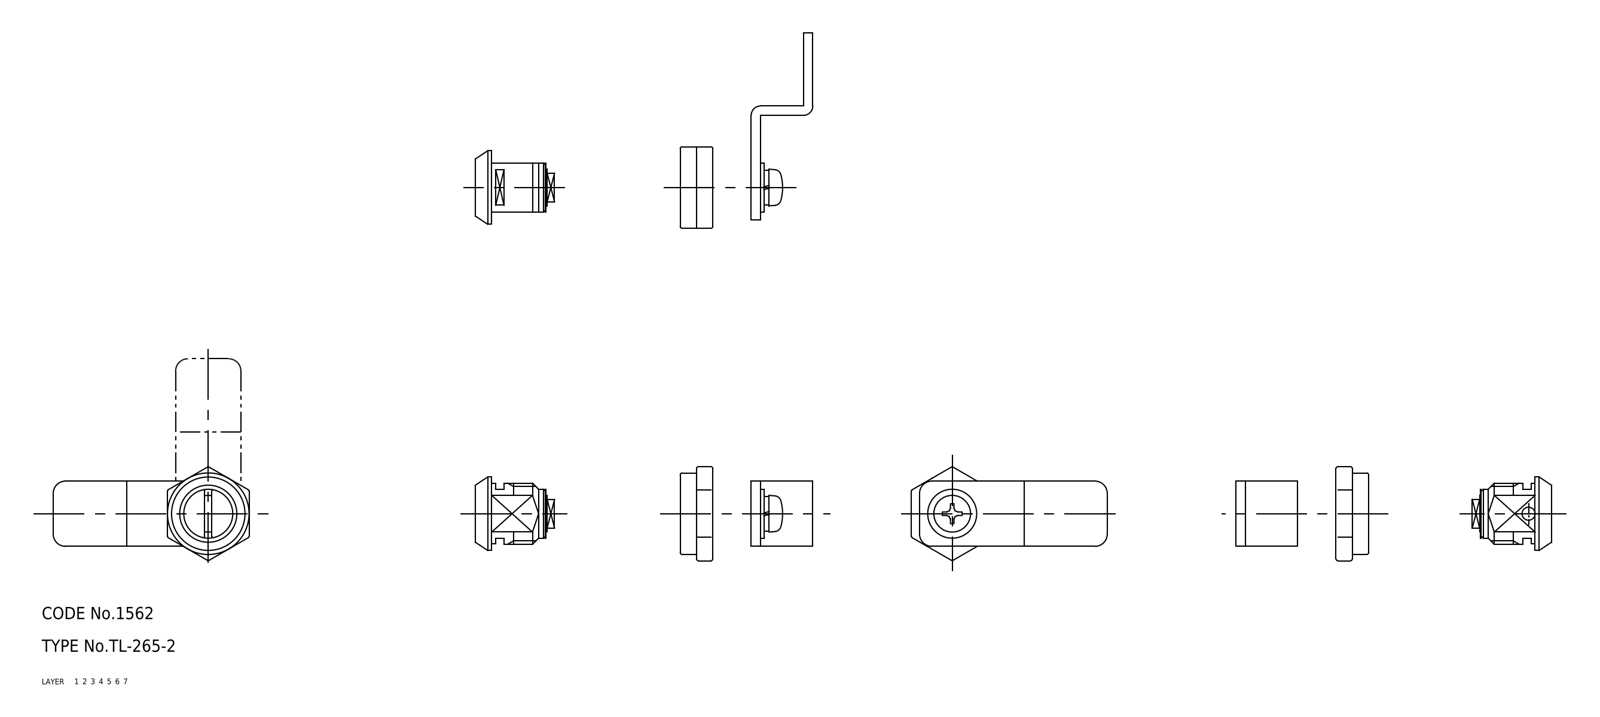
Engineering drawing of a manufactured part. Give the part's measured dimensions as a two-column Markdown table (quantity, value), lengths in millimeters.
| quantity | value |
| --- | --- |
| part name | shaft; screw; retainer; nut (+2 more) |
| STEP written by | CADfix (AUTOMOTIVE_DESIGN) |
| units | millimeters |
| bodies | 6 solids, 177 faces (0 planar, 0 cylindrical, 177 other) |
| overall size | 48 × 32.7 × 22.94 |
| volume | 6 061 mm³ |
| surface area | 6 456 mm² |
